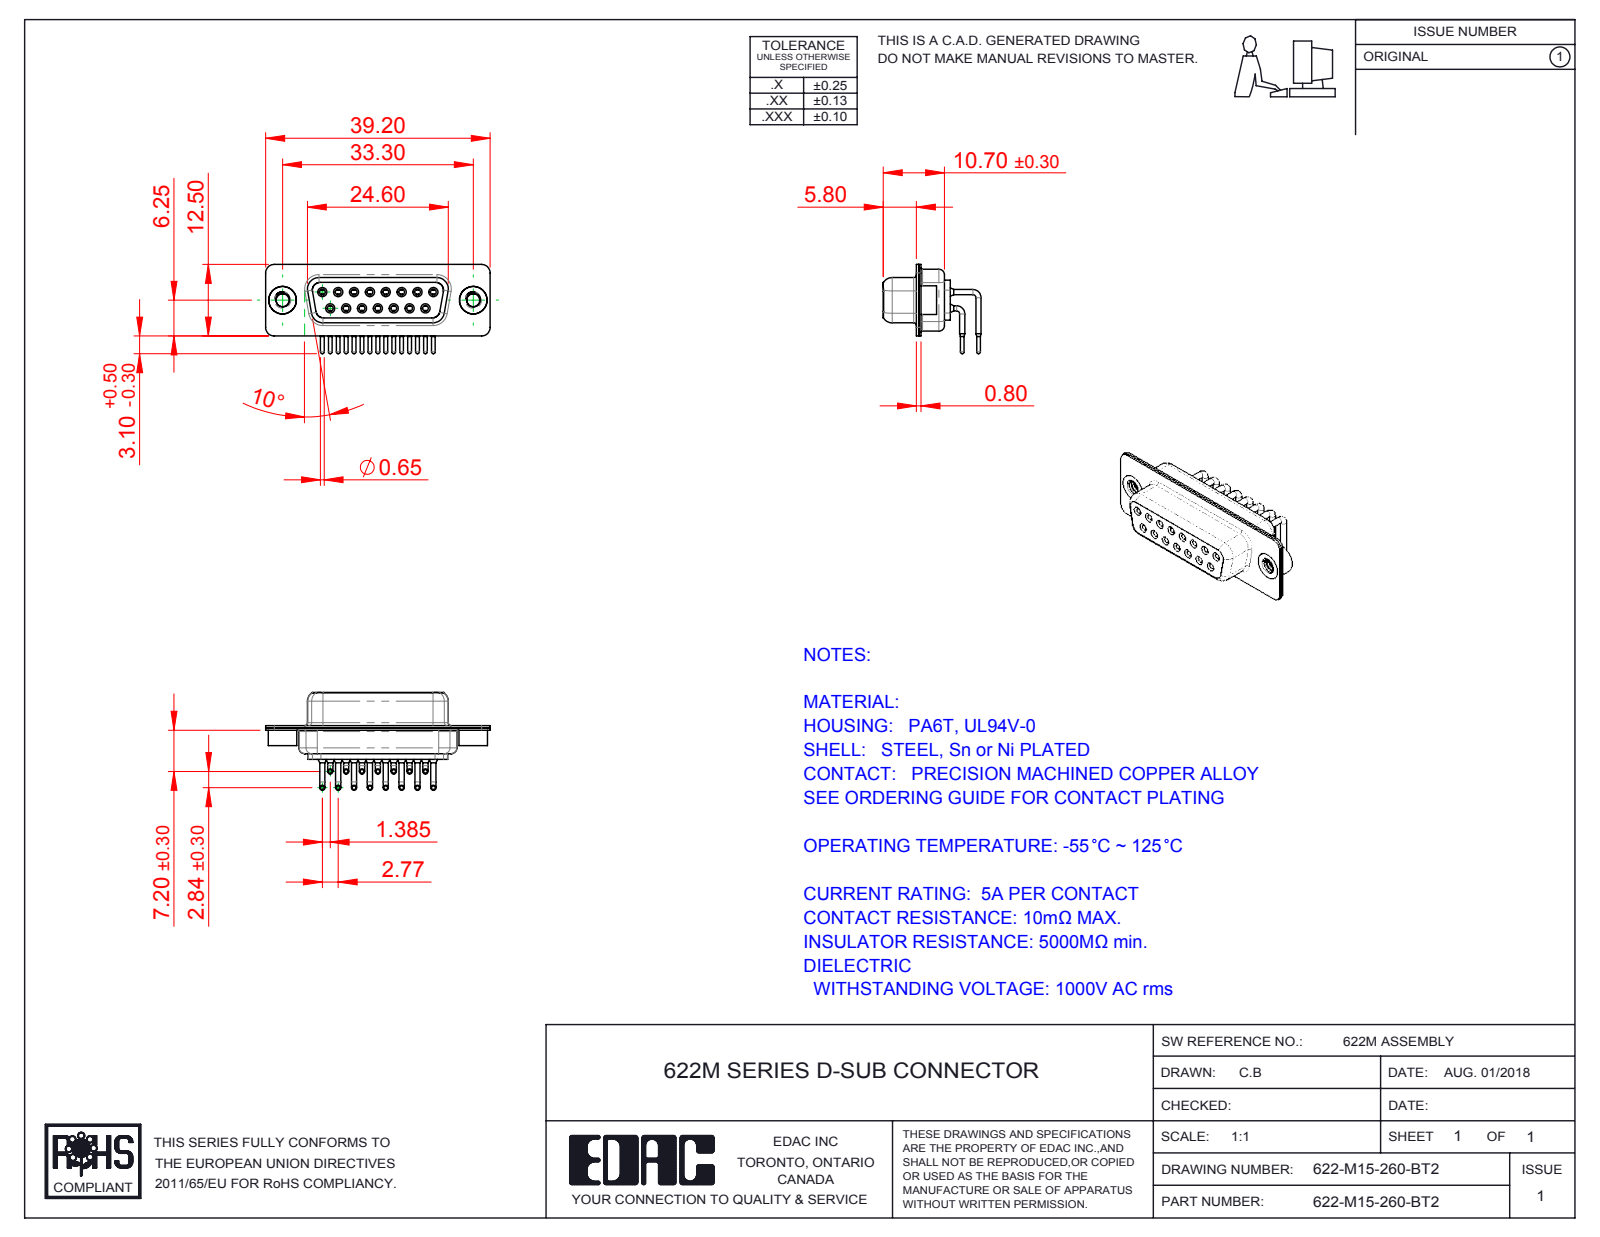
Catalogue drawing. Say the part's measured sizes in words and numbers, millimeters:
The part is named "622M Shell Front_15 Contacts; 622M Housing_15 Contacts; 622M Shell Rear_15 Contacts; 622M 4-40 Threaded Rivet (+3 more)". Its 3-D file was written by "SolidWorks 2016 (CONFIG_CONTROL_DESIGN)". It is 20 solids with 1074 faces: 292 planar, 482 cylindrical and 300 other. Overall it measures 39.2 by 17.09 by 15.6 millimeters. Its volume is 2 540 cubic millimeters and its surface area 6 418 square millimeters. Round holes: 15 of diameter 1, 15 of diameter 1.1, 15 of diameter 1.7, 15 of diameter 1.8, 15 of diameter 2, 2 of diameter 2.26, 2 of diameter 4, 2 of diameter 4.8. Round bosses or shafts: 30 of diameter 0.9, 15 of diameter 1.6, 15 of diameter 1.5, 15 of diameter 0.65, 2 of diameter 5, 2 of diameter 4.9. Partial cylindrical surfaces (rounded edges, fillets, slot ends): 16 of radius 1.5, 12 of radius 2, 8 of radius 1.35, 8 of radius 1.6, 4 of radius 0.25, 4 of radius 0.5, 4 of radius 0.6, 4 of radius 0.65. The main face-to-face distances are 0.4, 1.45, 8.95, 2.3, 6.2, 0.8, 1.9, 8.5, 0.45, 7.05. The hole center spacings are 3.16, 2.77, 5.54, 8.31, 11.08, 5.03, 5.04, 7.48.
